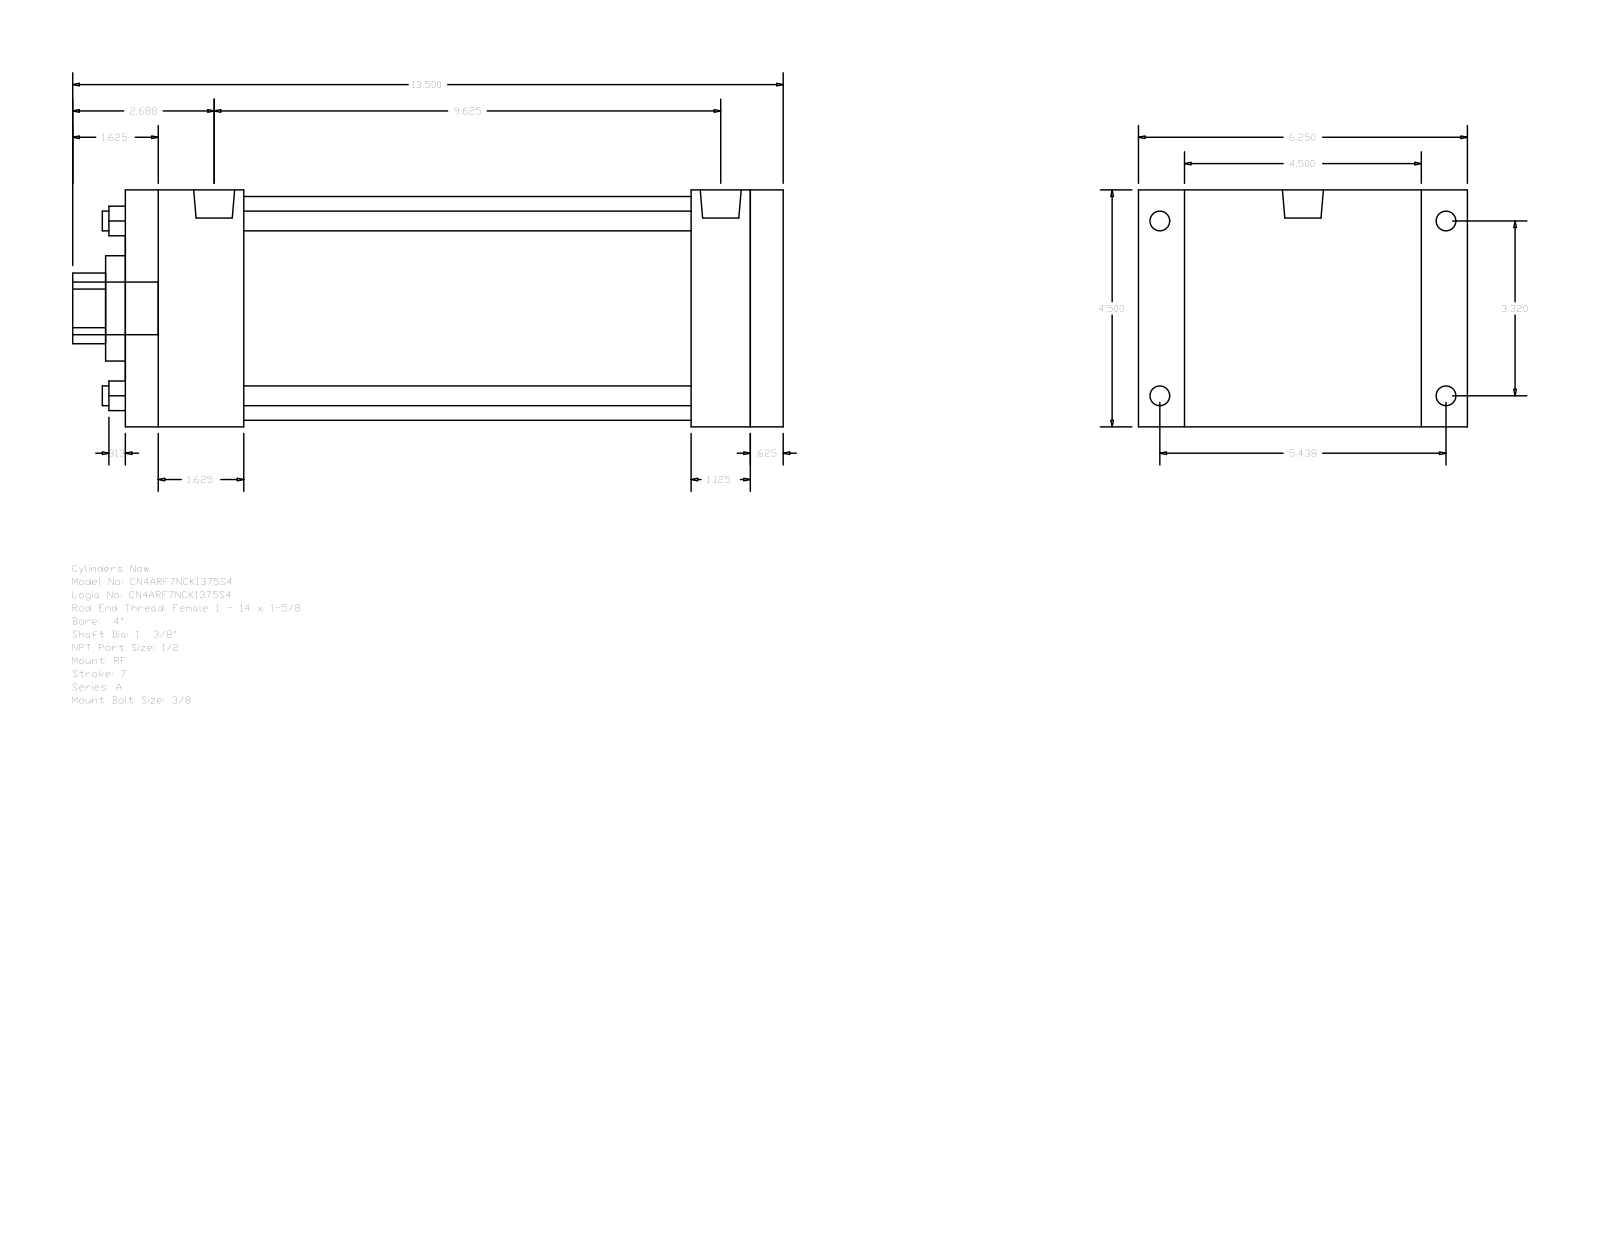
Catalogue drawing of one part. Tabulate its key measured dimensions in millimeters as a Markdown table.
| quantity | value |
| --- | --- |
| part name | A_RF__0400_1.375 |
| STEP written by | GSSL Pune (CONFIG_CONTROL_DESIGN) |
| units | millimeters |
| bodies | 0 solids, 92 faces (64 planar, 28 cylindrical, 0 other) |
| overall size | 342.9 × 158.75 × 114.3 |
| round holes (diameter × count) | 9.53 × 4, 34.92 × 1, 50.8 × 1, 107.95 × 1 |
| round bosses / shafts (diameter × count) | 9.53 × 4, 8.73 × 4, 19.77 × 2, 25.4 × 1 |
| partial cylindrical surfaces (radius × count) | 17.06 × 1 |
| main face-to-face distances | 114.3, 317.5, 15.88, 301.62, 28.57, 22.23, 136.53, 273.05, 44.45, 57.15 |
| hole center spacings | 59.62, 84.32, 119.25 |
